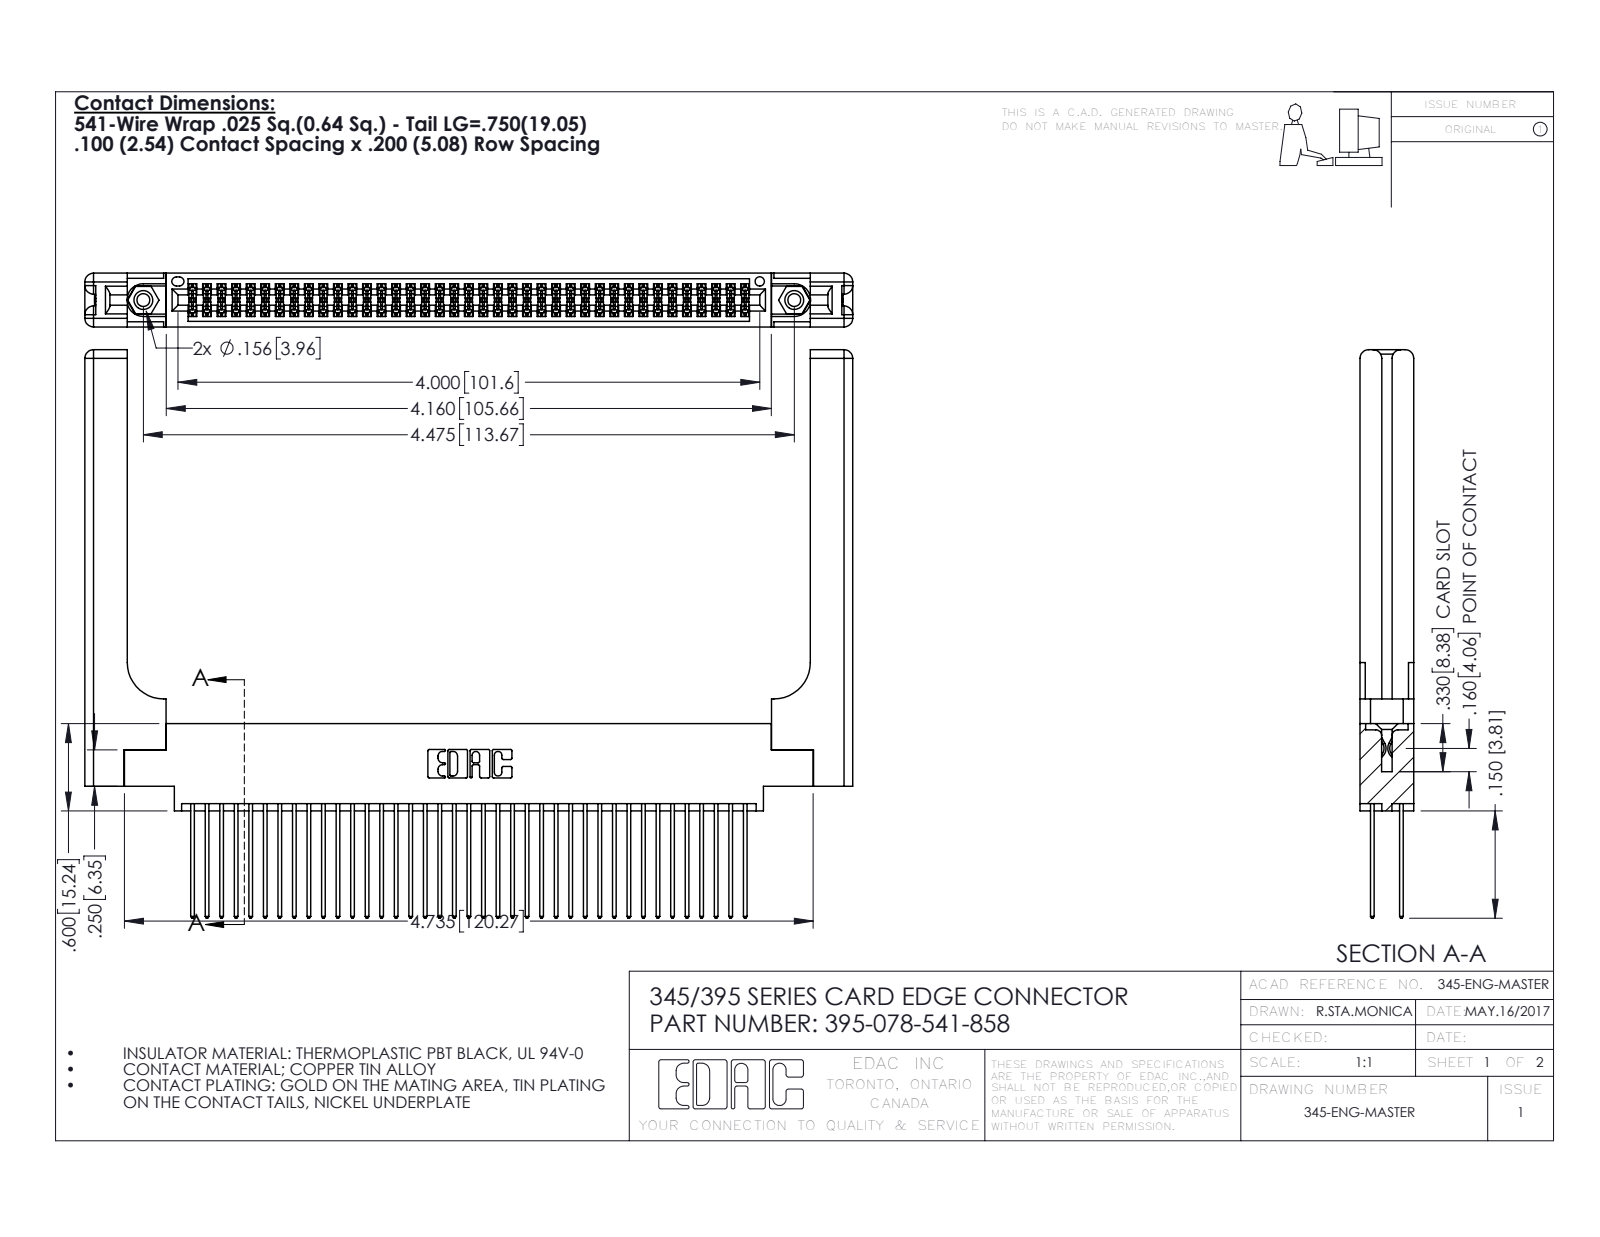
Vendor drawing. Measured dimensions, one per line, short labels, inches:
name: 345-292-001_345-293-141; 345 Part_0.170 Offset - 0.156 Dia-TH; 345-250-001_345-250-001-102; 345-220-058_345-220-058 (+1 more)
written by: SolidWorks 2016 (CONFIG_CONTROL_DESIGN)
unit: in
bodies: 83 solids, 4286 faces (2806 planar, 1420 cylindrical, 60 other)
size: 5.279 × 3.907 × 0.37
volume: 1.331 in³; area: 41.78 in²
holes: 2× ⌀0.089, 2× ⌀0.125, 2× ⌀0.156, 1× ⌀0.064
bosses: 2× ⌀0.155
rounds: 117× R0.006, 78× R0.01, 22× R0.01, 16× R0.06, 6× R0.007, 6× R0.031, 3× R0.026, 2× R0.014
face distances: 0.072, 0.298, 0.37, 0.098, 0.272, 0.025, 0.2, 0.225, 0.175, 0.148
hole spacings: 0.27, 4.239, 4.475
